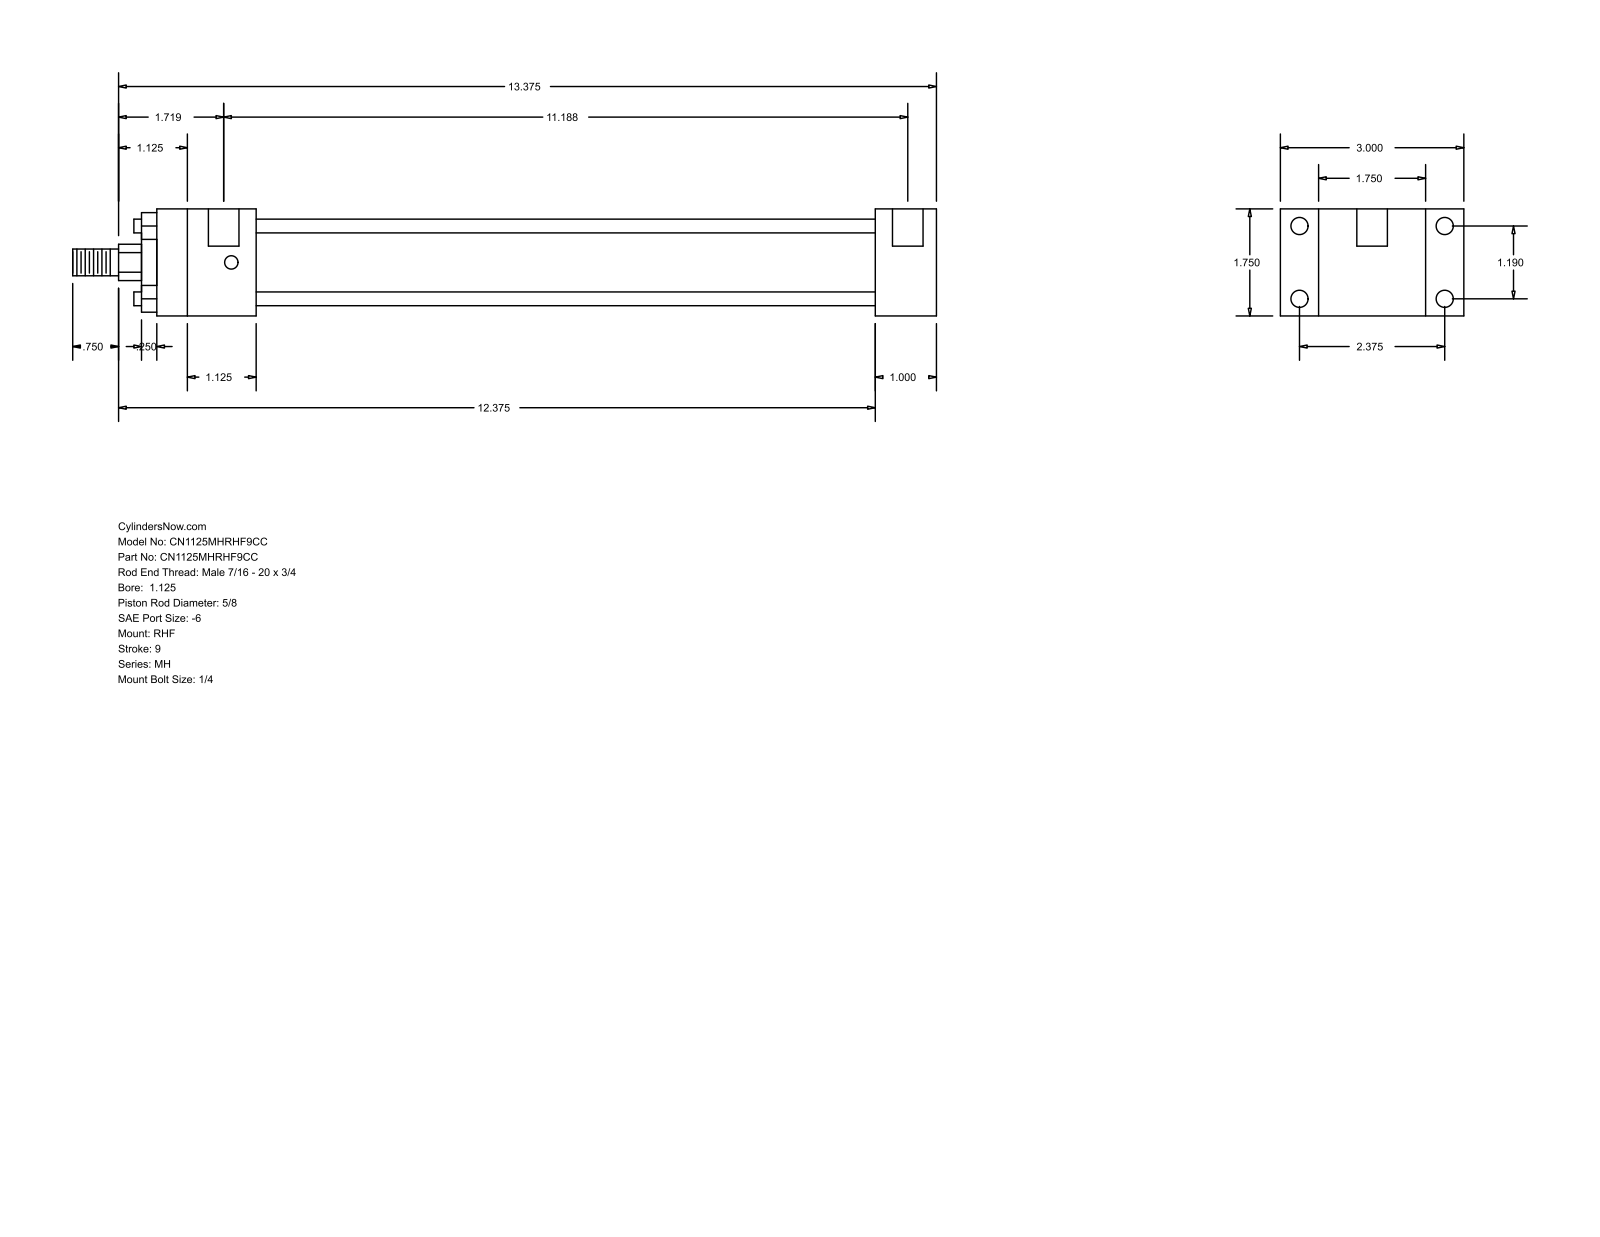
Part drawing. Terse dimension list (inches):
name: MH_RHF__0112_0.625
written by: GSSL Pune (CONFIG_CONTROL_DESIGN)
unit: in
bodies: 0 solids, 88 faces (60 planar, 28 cylindrical, 0 other)
size: 14.125 × 3 × 1.75
holes: 4× ⌀0.219, 4× ⌀0.281, 2× ⌀0.5
bosses: 4× ⌀0.225, 1× ⌀1.375, 1× ⌀1.125, 1× ⌀0.625, 1× ⌀0.437
rounds: 1× R0.297
face distances: 1.75, 0.625, 2.375, 1, 3, 10.125, 11.125, 1.625, 11.75, 12.75
hole spacings: 1.19, 2.375, 2.656, 11.063, 0.125, 11.187
